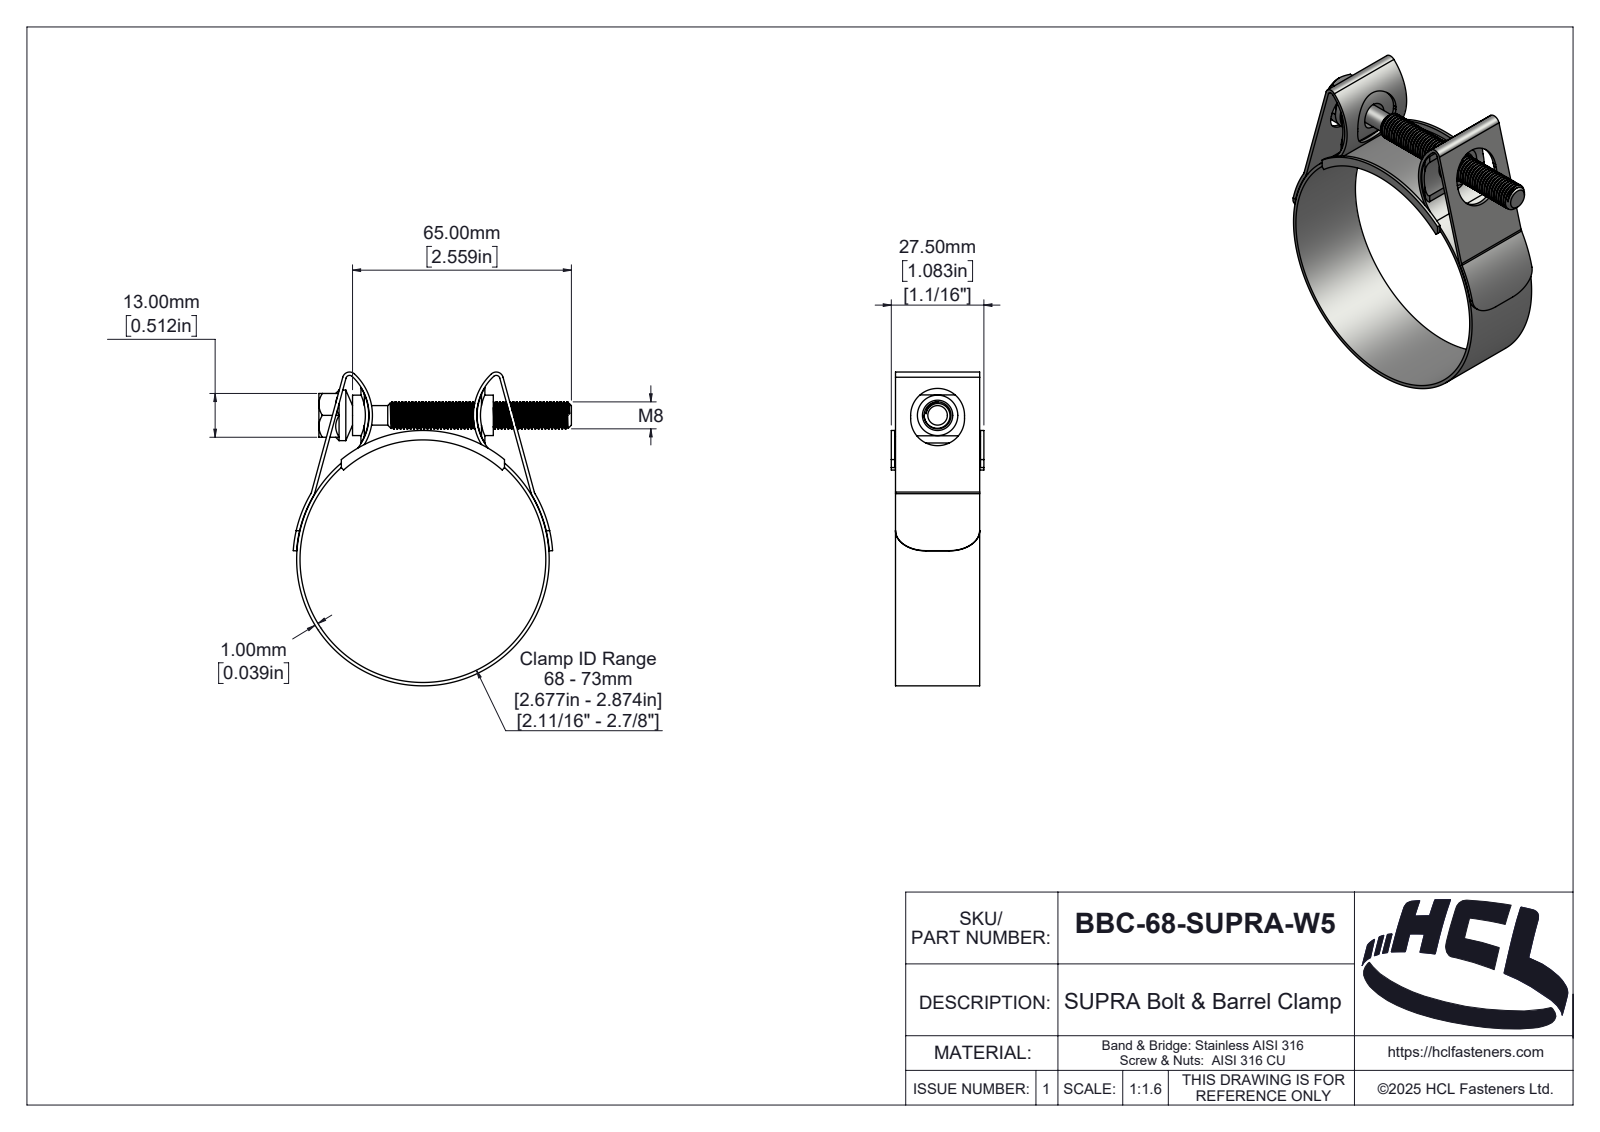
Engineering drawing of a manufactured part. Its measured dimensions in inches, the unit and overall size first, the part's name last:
Units: inches
Overall size (bounding box): 3.667 × 3.252 × 1.083
Round holes (diameter × count): ⌀2.874 ×1
Round bosses / shafts (diameter × count): ⌀2.953 ×1, ⌀0.591 ×1, ⌀0.472 ×1, ⌀0.315 ×1, ⌀0.228 ×1
Partial cylindrical surfaces — rounded edges, fillets, slot ends (radius × count): R0.039 ×4, R0.043 ×2, R0.079 ×2, R0.083 ×2, R0.118 ×2, R0.315 ×2, R0.579 ×2, R0.619 ×2
Main face-to-face distances: 0.039, 0.984, 0.049, 1.033, 1.043, 0.994, 1.083, 0.512, 0.098, 1.547
Volume: 0.898 in³ · Surface area: 39.12 in²
Bodies: 5 solids, 351 faces (46 planar, 218 cylindrical, 87 other)
Part name (STEP PRODUCT): BBC-68-SUPRA-W5
STEP written by: SolidWorks 2025 (AUTOMOTIVE_DESIGN)
